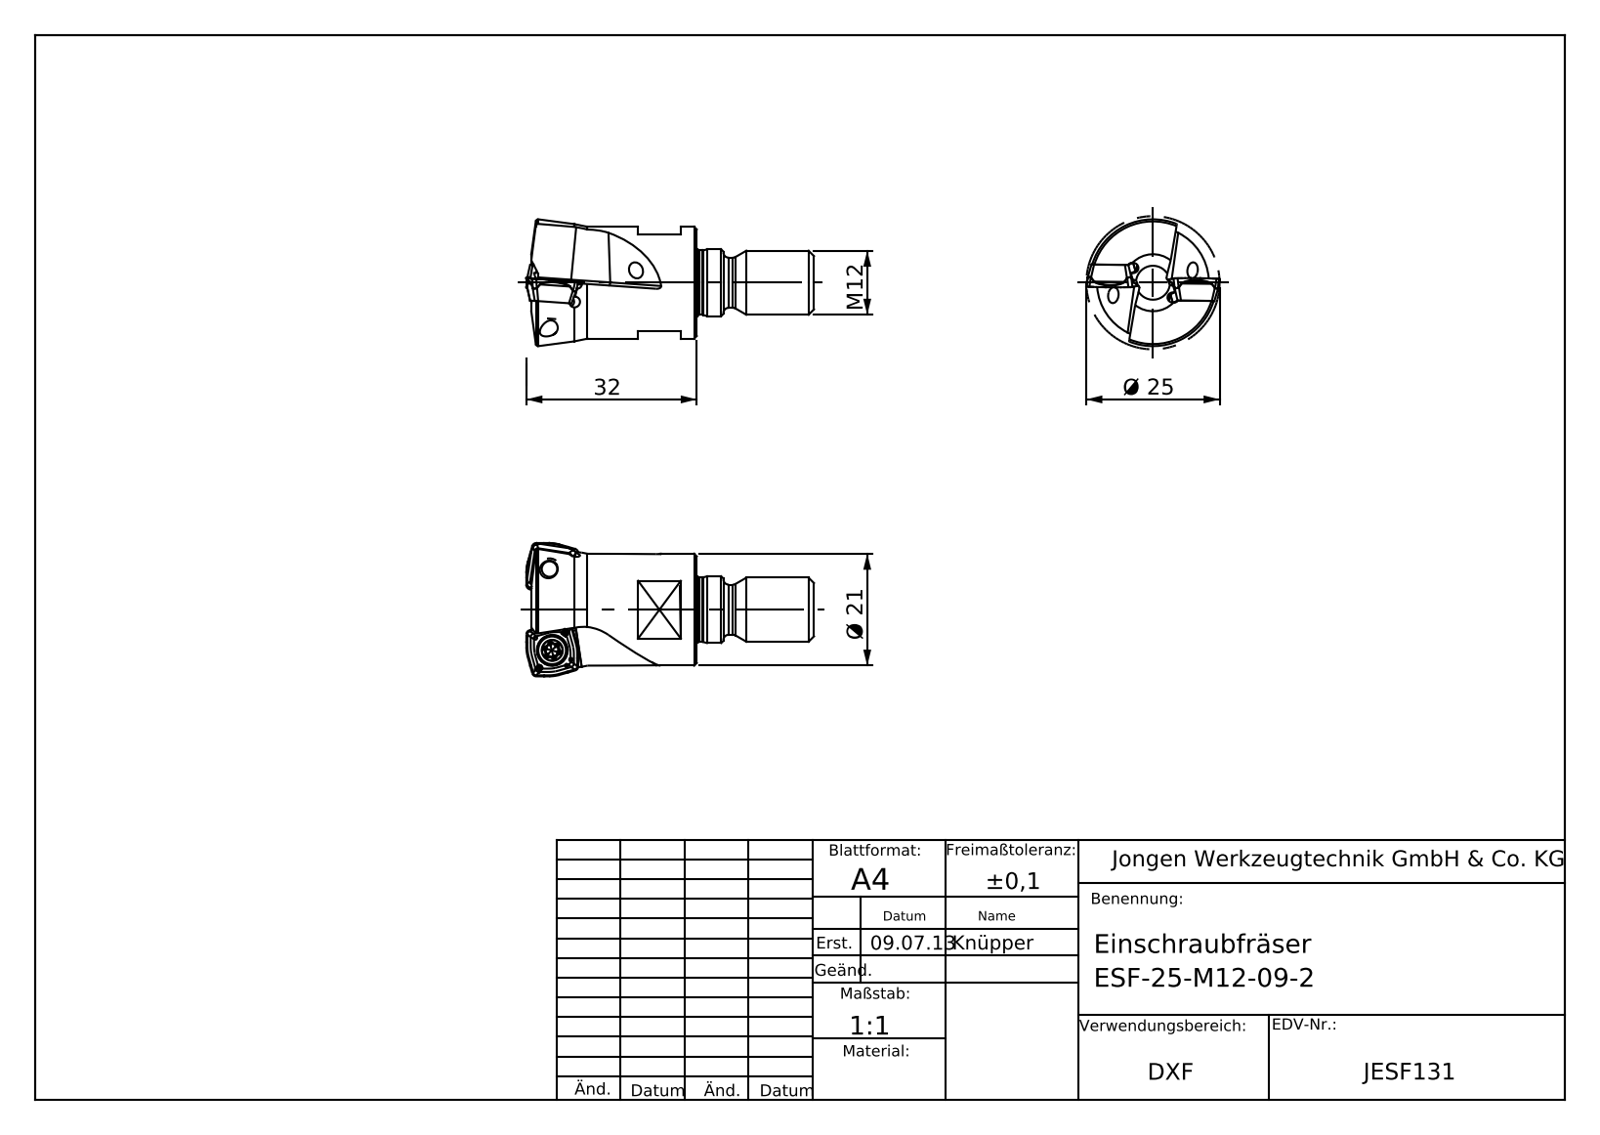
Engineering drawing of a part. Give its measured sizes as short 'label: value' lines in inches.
name: ESF-25-M12-09-2
written by: SolidWorks 2013 (AUTOMOTIVE_DESIGN)
unit: in
bodies: 1 solid, 74 faces (27 planar, 23 cylindrical, 24 other)
size: 2.125 × 0.985 × 0.985
volume: 0.776 in³; area: 7.177 in²
holes: 2× ⌀0.118, 1× ⌀0.13
bosses: 1× ⌀0.827, 1× ⌀0.492, 1× ⌀0.476, 1× ⌀0.472, 1× ⌀0.37
rounds: 4× R0.02, 4× R0.031, 2× R0.039, 2× R0.079
face distances: 0.709, 0.866, 2.039, 1.173, 0.315, 0.984, 0.118, 1.055, 1.299, 0.433
